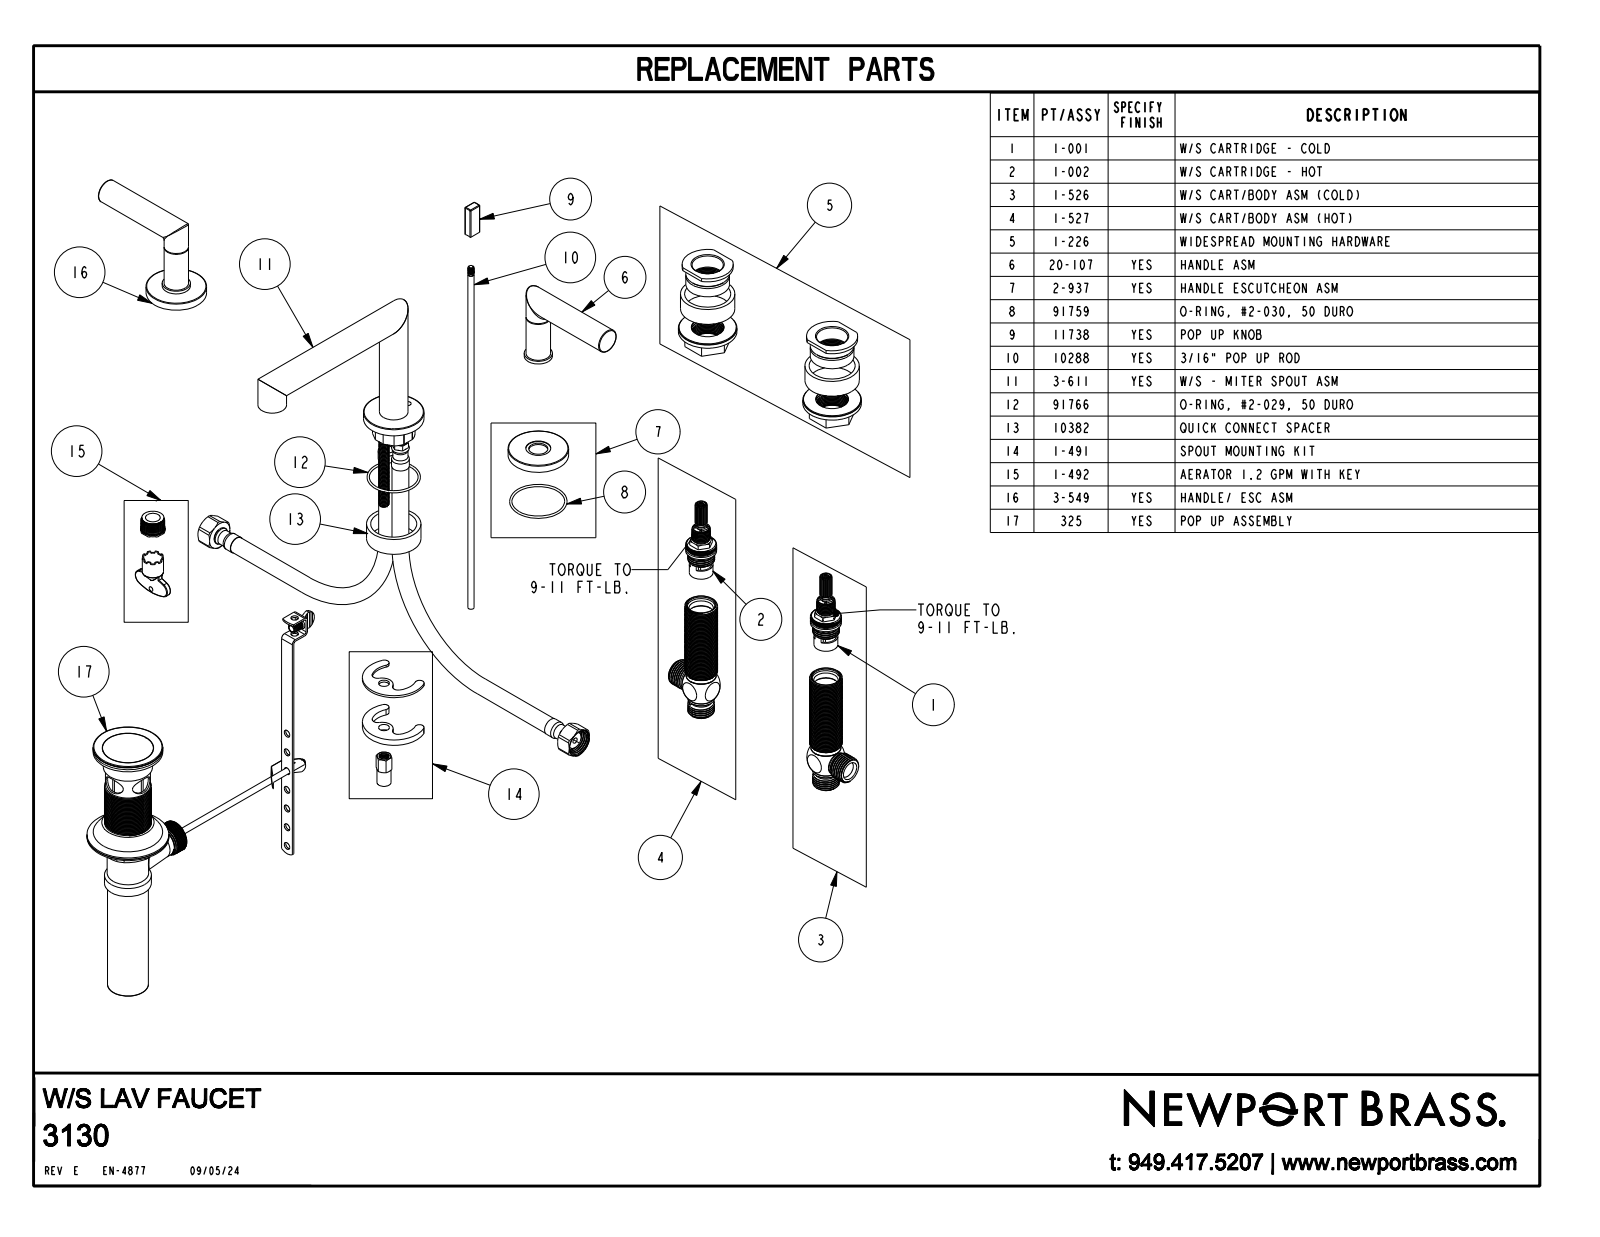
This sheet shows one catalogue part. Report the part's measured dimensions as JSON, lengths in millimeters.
{"part_name": "3130", "step_written_by": "CREO PARAMETRIC BY PTC INC, 2018400 (CONFIG_CONTROL_DESIGN)", "units": "millimeters", "bodies": {"solids": 3, "faces": 95, "planar": 23, "cylindrical": 44, "other": 28}, "overall_size": [355.6, 168, 107.1], "volume_mm3": 201100, "surface_area_mm2": 47430, "round_bosses_or_shafts": [[47, 3], [22.2, 3], [19.1, 3], [21.8, 2], [12.9, 2]], "partial_cylinders_radius": [[0.5, 6], [11.9, 1], [22.3, 1]], "face_to_face_distances": [6.4, 174.6, 181, 79.5, 73.1, 43.2, 44, 36.9, 37.6, 0.8]}
